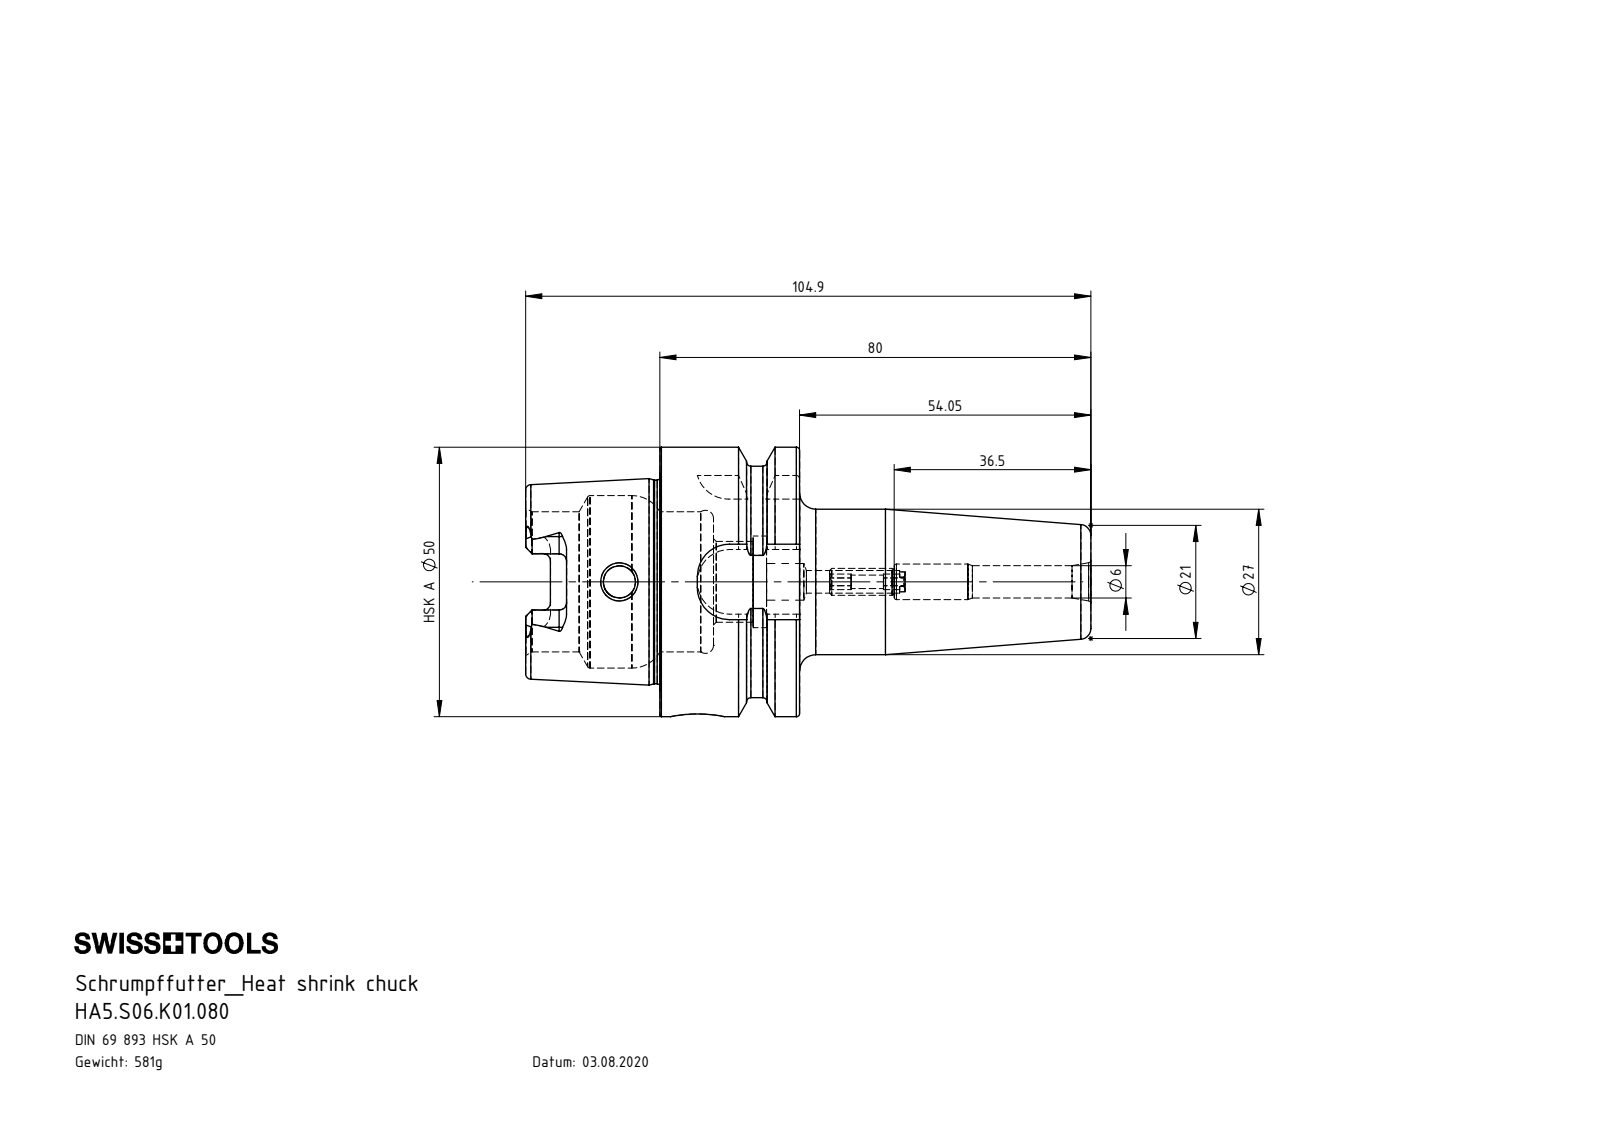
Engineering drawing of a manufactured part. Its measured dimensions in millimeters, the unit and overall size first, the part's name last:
Units: millimetres
Overall size (bounding box): 104.9 × 50 × 50
Round holes (diameter × count): ⌀6 ×2, ⌀2.5 ×1, ⌀4.2 ×1, ⌀6.6 ×1, ⌀6.8 ×1, ⌀10 ×1, ⌀15 ×1, ⌀17 ×1, ⌀26 ×1, ⌀32 ×1
Round bosses / shafts (diameter × count): ⌀50 ×1, ⌀42.95 ×1, ⌀37.81 ×1, ⌀27 ×1, ⌀5 ×1
Partial cylindrical surfaces — rounded edges, fillets, slot ends (radius × count): R1.4 ×6, R2.38 ×4, R6 ×4
Main face-to-face distances: 25.95, 9.95, 16, 24.9, 34.85, 50.85, 41.8, 44.7, 19.8, 9.85
Volume: 74 068 mm³ · Surface area: 20 291 mm²
Bodies: 2 solids, 232 faces (80 planar, 59 cylindrical, 93 other)
Part name (STEP PRODUCT): HA5.S06.K01.080; ERU-AN1.K01.014_A; HA5-S06.K01.080_A_Fertigbearbeitung
STEP written by: SolidWorks 2022 (CONFIG_CONTROL_DESIGN)
